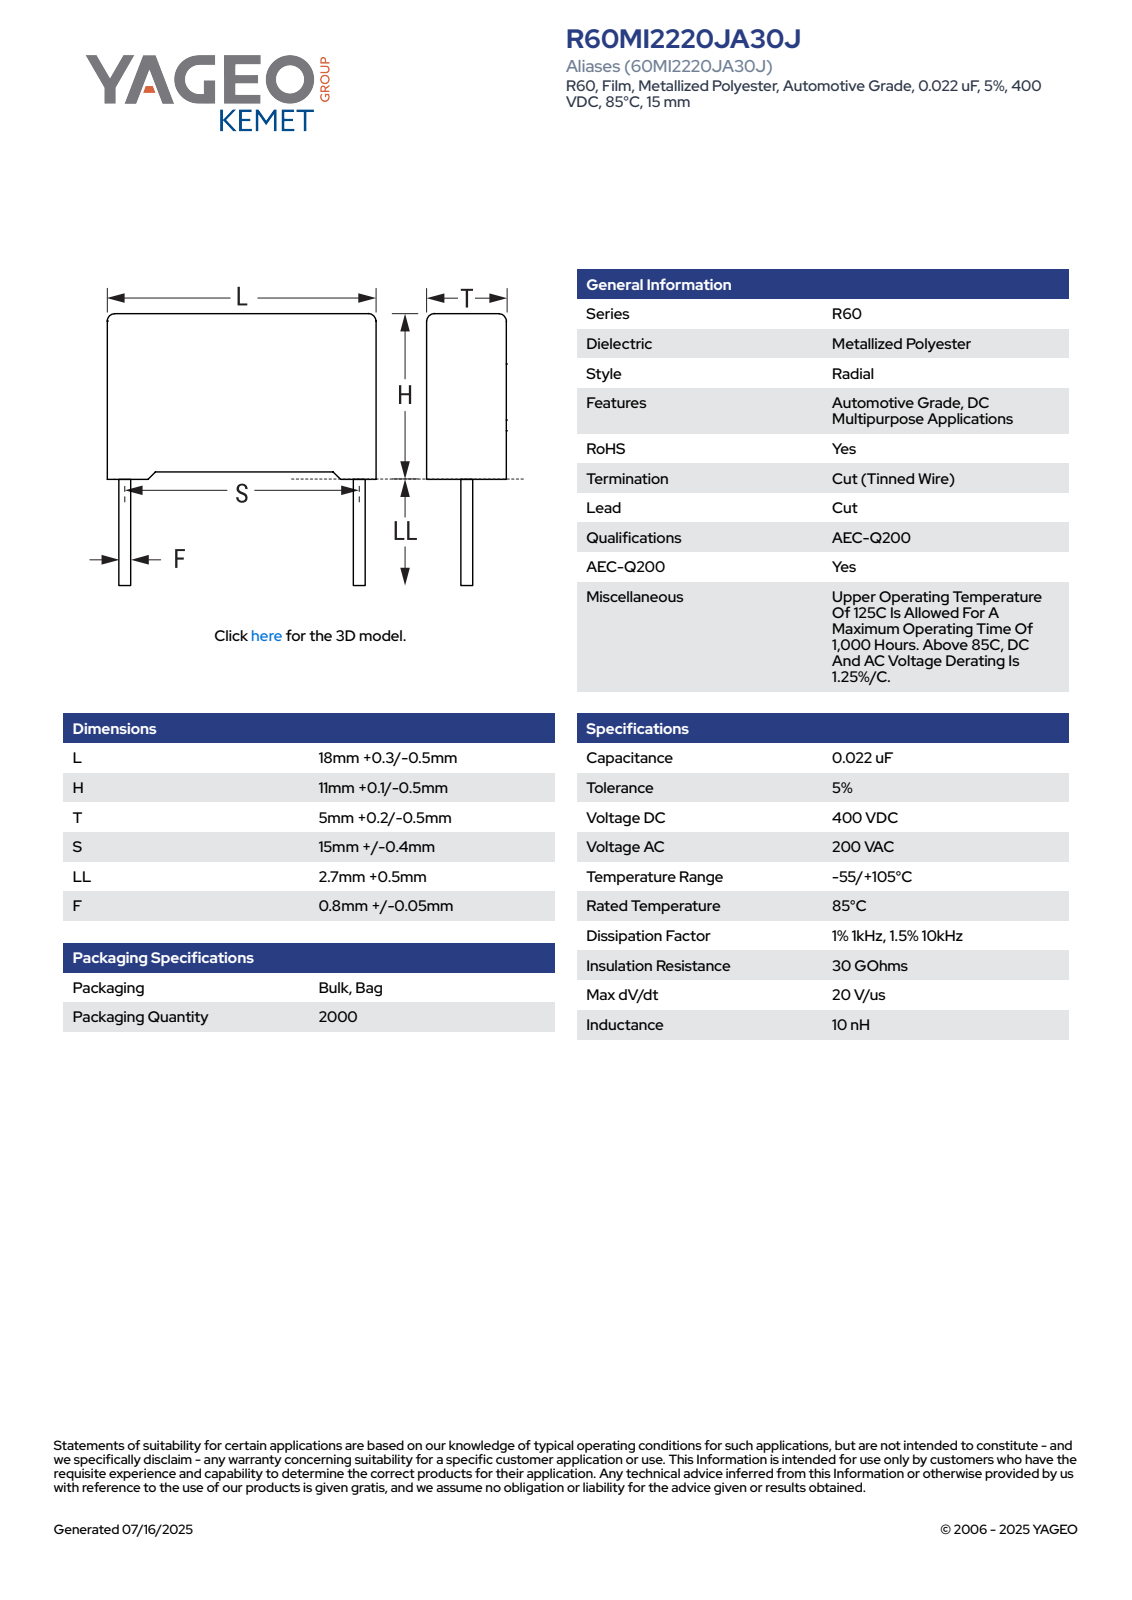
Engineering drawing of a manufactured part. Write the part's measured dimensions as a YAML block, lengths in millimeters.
part_name: "CFR_RB2_18X11X5_L18.3H11.1T5.2S15LL3.2F0.85"
step_written_by: "SolidWorks 2021 (AUTOMOTIVE_DESIGN)"
units: millimeters
bodies: {solids: 4, faces: 85, planar: 77, cylindrical: 8, other: 0}
overall_size: [18.3, 14.3, 5.21]
volume: 1002
surface_area: 762
round_bosses_or_shafts:
  - {diameter: 0.85, count: 2}
partial_cylinders:
  - {radius: 0.5, count: 4}
face_to_face_distances: [5.2, 10.35, 18.3, 0.61, 4.59, 0.37, 10.72, 0.38, 0.75, 11.1]
